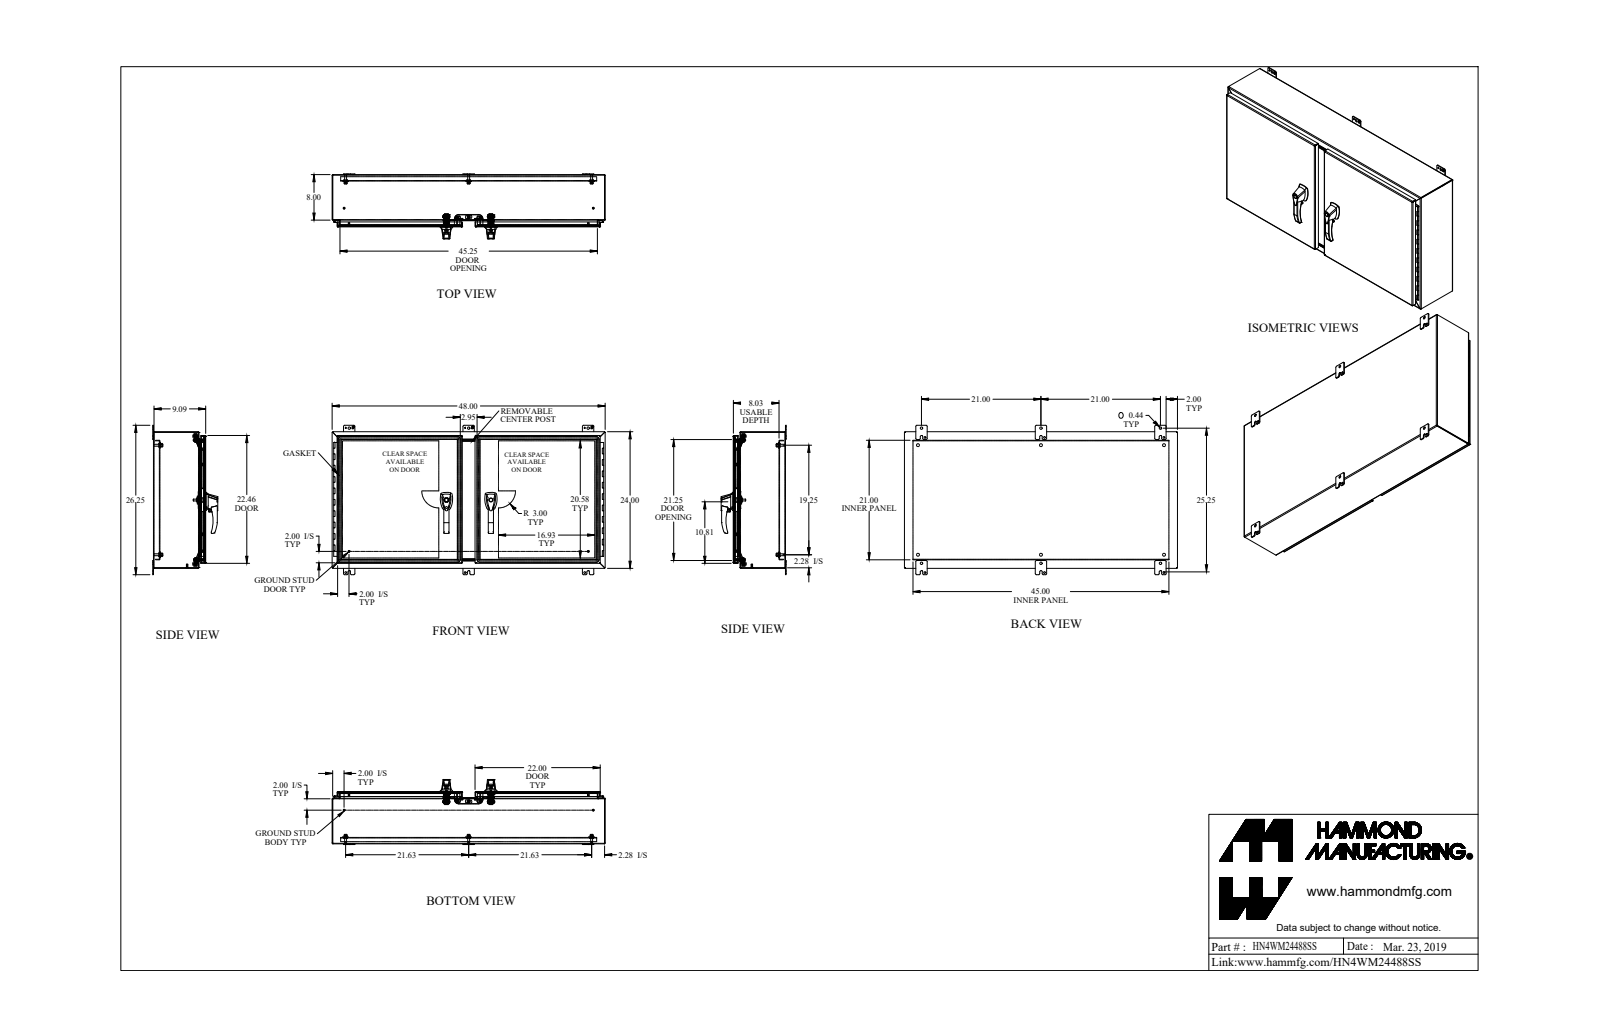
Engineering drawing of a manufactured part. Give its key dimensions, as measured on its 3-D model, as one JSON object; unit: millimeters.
{"part_name": "HN4WM24488SS", "step_written_by": "SolidWorks 2018 (AUTOMOTIVE_DESIGN)", "units": "millimeters", "bodies": {"solids": 108, "faces": 2624, "planar": 1243, "cylindrical": 1101, "other": 280}, "overall_size": [1219.2, 666.8, 290.2], "volume_mm3": 8742000, "surface_area_mm2": 7085000, "round_holes": [[6.4, 9], [8, 9], [7.7, 8], [5.1, 6], [7.8, 6], [12.7, 6], [7.1, 4], [8, 4], [9.9, 4], [11.3, 4], [6.5, 3], [7.1, 3]], "round_bosses_or_shafts": [[25.4, 9], [16.5, 6], [9.5, 6], [8.4, 6], [7.4, 6], [19.1, 4], [15.9, 4], [11.2, 4]], "partial_cylinders_radius": [[3.2, 35], [0.5, 32], [4.8, 27], [6.4, 26], [1.5, 22], [12.7, 22], [1.2, 19], [3.6, 19]], "face_to_face_distances": [2.4, 26.2, 2.4, 230.9, 228.5, 23.8, 233.3, 230.9, 28.6, 202.3], "hole_center_spacings": [198.5, 152.4, 1181.9, 28.6, 32.7, 51.8, 184.8, 200.5]}
